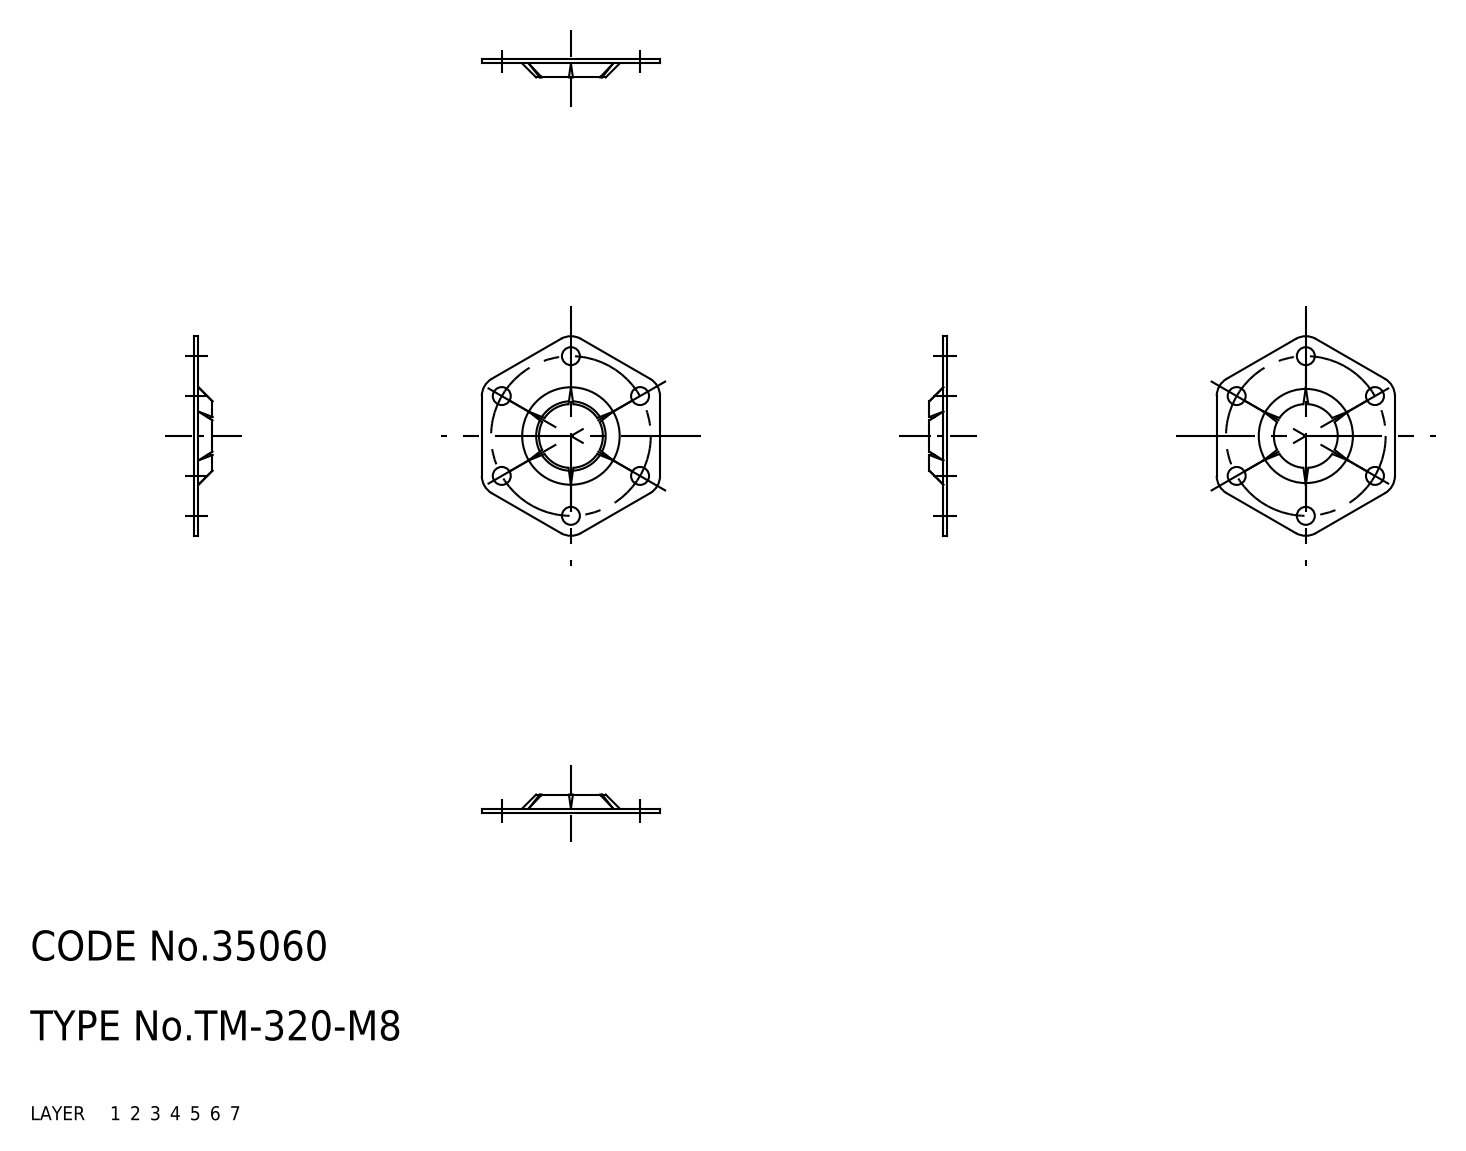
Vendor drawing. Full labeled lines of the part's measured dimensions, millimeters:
Part name (STEP PRODUCT): 67111930
STEP written by: CADfix (AUTOMOTIVE_DESIGN)
Units: millimetres
Bodies: 1 solid, 56 faces (0 planar, 0 cylindrical, 56 other)
Overall size (bounding box): 20 × 17.86 × 1.8
Volume: 95 mm³ · Surface area: 530 mm²
